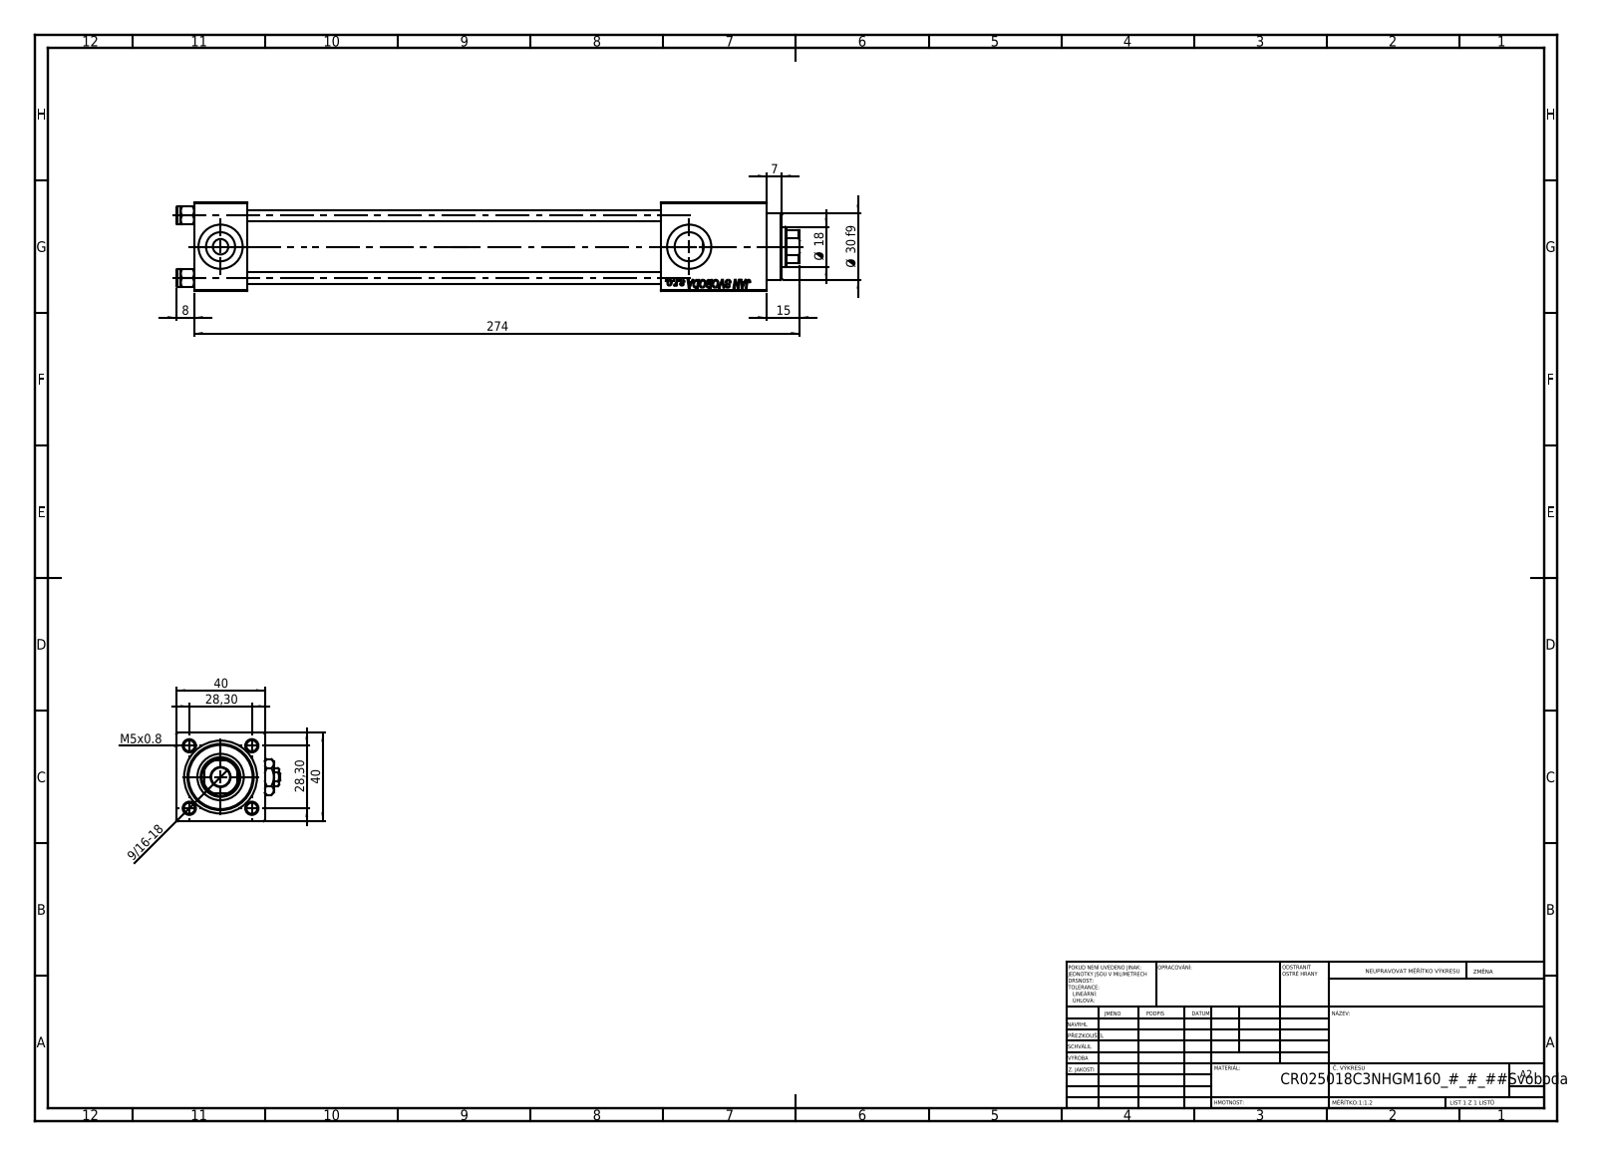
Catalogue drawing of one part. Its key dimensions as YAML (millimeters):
part_name: "Zatka_pro_OIL_PORT; NUT_M5_C; V215CR_VCP_C; V215_VC_A (+2 more)"
step_written_by: "SolidWorks 2019 (CONFIG_CONTROL_DESIGN)"
units: millimeters
bodies: {solids: 13, faces: 1245, planar: 571, cylindrical: 96, other: 578}
overall_size: [282, 47, 40]
volume: 232159
surface_area: 99828
round_holes:
  - {diameter: 5, count: 4}
  - {diameter: 20, count: 3}
  - {diameter: 7, count: 2}
  - {diameter: 13.16, count: 2}
  - {diameter: 8.5, count: 1}
  - {diameter: 18, count: 1}
  - {diameter: 21, count: 1}
  - {diameter: 25, count: 1}
  - {diameter: 30, count: 1}
round_bosses_or_shafts:
  - {diameter: 8, count: 4}
  - {diameter: 31, count: 1}
partial_cylinders:
  - {radius: 8.5, count: 1}
face_to_face_distances: [40, 24, 39.8, 211, 187, 230.3, 206.3, 19.3, 48, 259]
hole_center_spacings: [20.01, 28.3, 40.02, 212]
